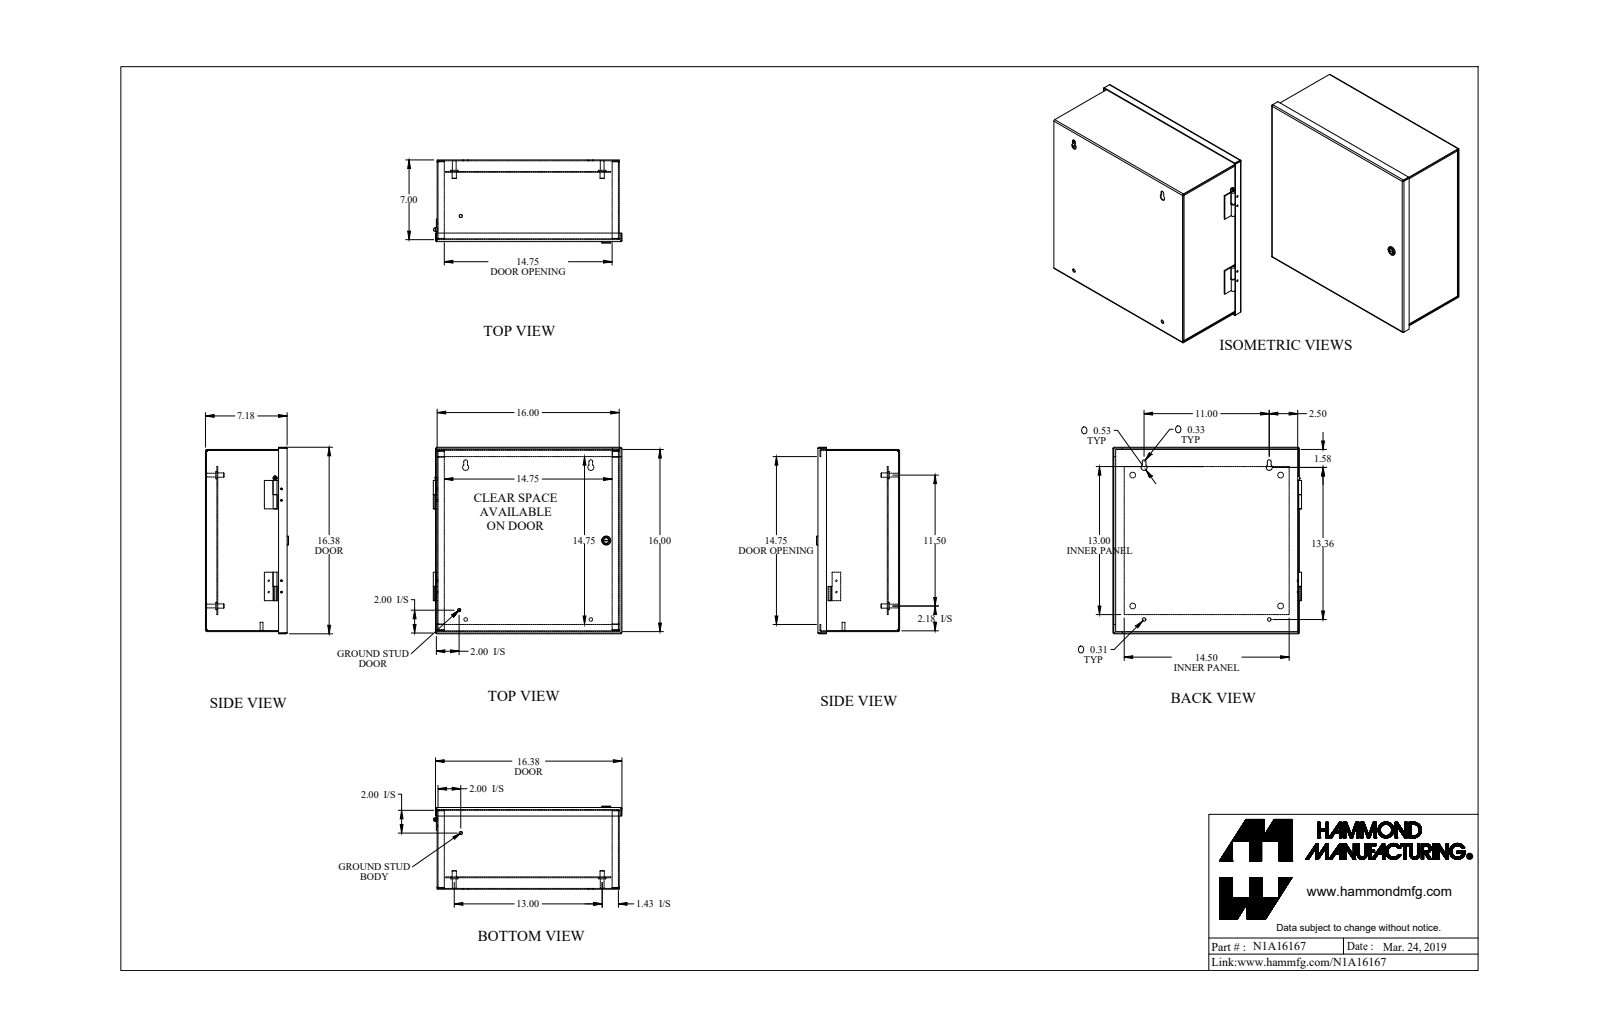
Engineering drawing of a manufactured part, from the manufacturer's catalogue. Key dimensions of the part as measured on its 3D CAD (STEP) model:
Part name (STEP PRODUCT): N1A16167
STEP written by: SolidWorks 2018 (AUTOMOTIVE_DESIGN)
Units: inches
Bodies: 23 solids, 520 faces (294 planar, 182 cylindrical, 44 other)
Overall size (bounding box): 16.574 × 16.384 × 7.299
Volume: 92.91 in³ · Surface area: 2 587 in²
Round holes (diameter × count): ⌀0.14 ×8, ⌀0.5 ×4, ⌀0.307 ×2, ⌀0.312 ×2, ⌀0.445 ×2, ⌀0.17 ×1, ⌀0.187 ×1, ⌀0.516 ×1
Round bosses / shafts (diameter × count): ⌀0.128 ×8, ⌀0.375 ×5, ⌀0.65 ×4, ⌀0.33 ×4, ⌀1 ×2, ⌀0.281 ×2, ⌀0.25 ×2, ⌀0.788 ×1
Partial cylindrical surfaces — rounded edges, fillets, slot ends (radius × count): R0.036 ×16, R0.108 ×16, R0.06 ×2, R0.153 ×2, R0.164 ×2, R0.266 ×2, R0.03 ×1, R0.125 ×1
Main face-to-face distances: 0.072, 7.105, 15.928, 1.009, 6.096, 7.033, 7.177, 16, 15.856, 1.081
Hole centre spacings: 1, 1.119, 1.104, 1.553, 2.031, 5.761, 8.062, 8.062
